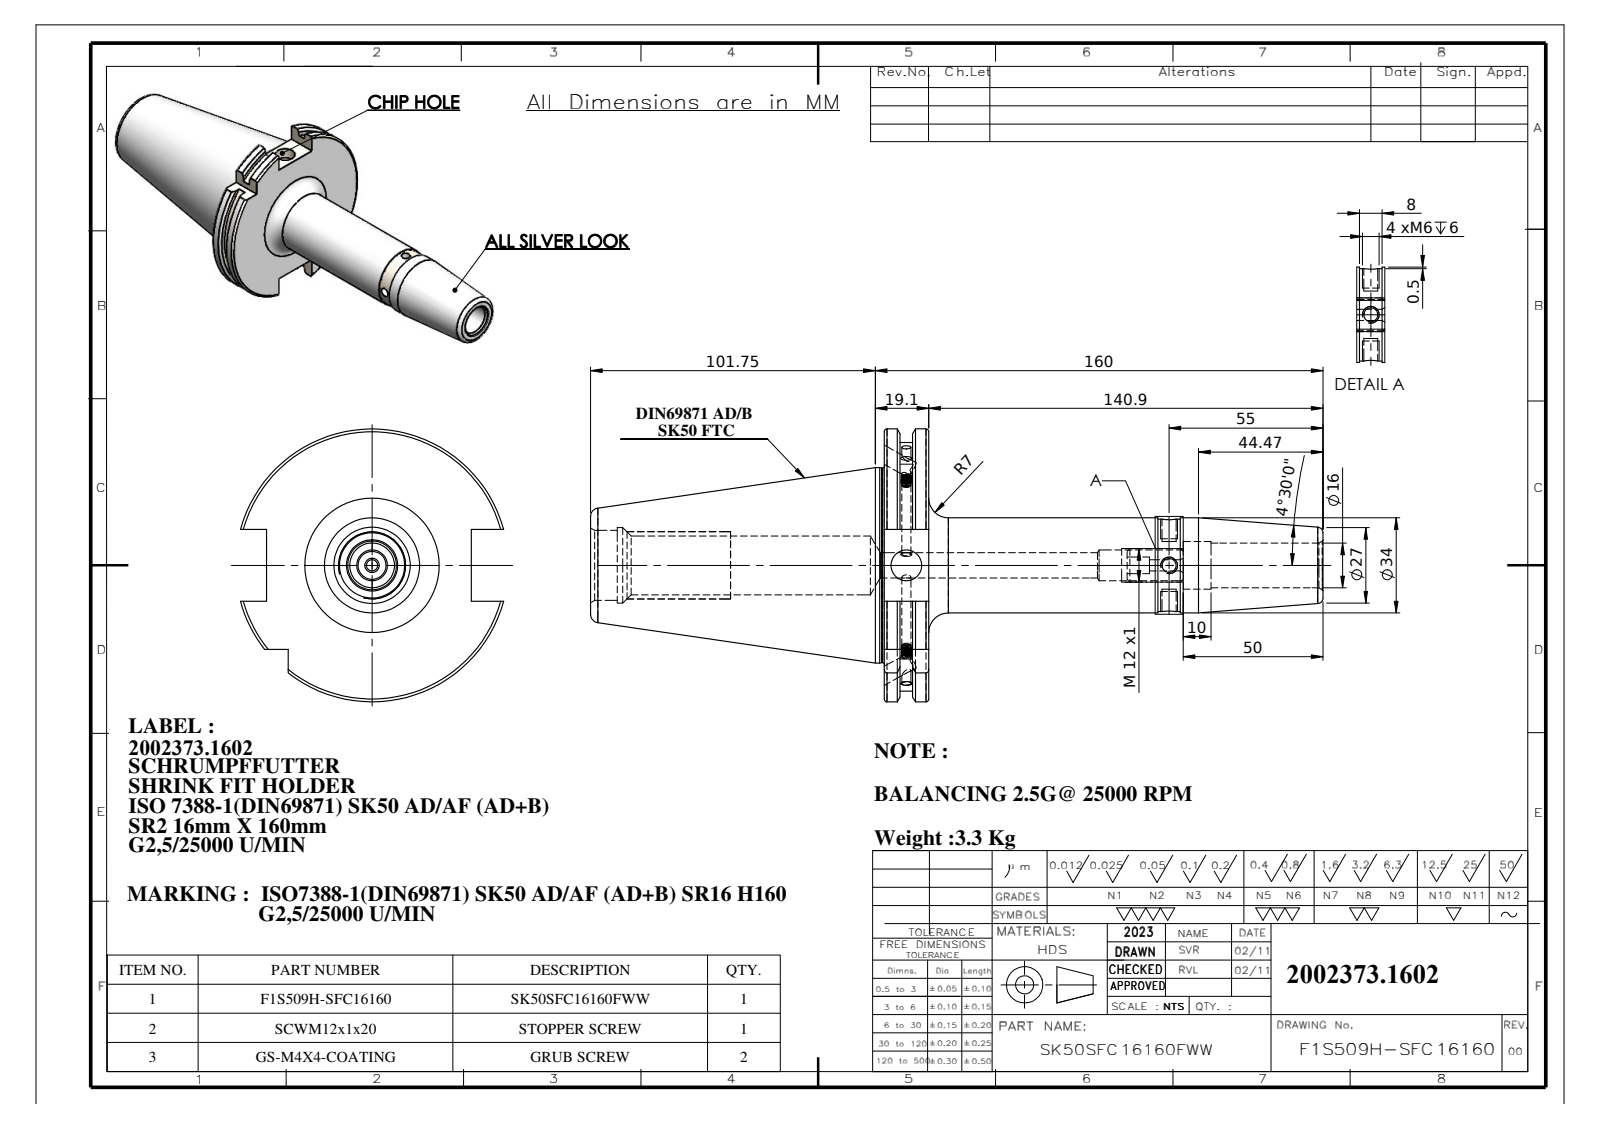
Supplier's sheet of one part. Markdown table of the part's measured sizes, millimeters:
| quantity | value |
| --- | --- |
| part name | 91506-SR216160 |
| STEP written by | SolidWorks 2018 (AUTOMOTIVE_DESIGN) |
| units | millimeters |
| bodies | 1 solid, 122 faces (29 planar, 53 cylindrical, 40 other) |
| overall size | 261.75 × 97.5 × 94.05 |
| volume | 432 948 mm³ |
| surface area | 63 750 mm² |
| round holes (diameter × count) | 5 × 2, 6 × 2, 11 × 2, 3.3 × 1, 15.99 × 1, 17 × 1, 21 × 1, 25 × 1, 27 × 1 |
| round bosses / shafts (diameter × count) | 69.85 × 1, 69.45 × 1, 34 × 1 |
| partial cylindrical surfaces (radius × count) | 44.9 × 1, 48.75 × 1 |
| main face-to-face distances | 15.9, 5.66, 10.24, 10.14, 4.48, 5.76, 104.95, 110.61, 115.09, 120.85 |
| hole center spacings | 93.9 |
